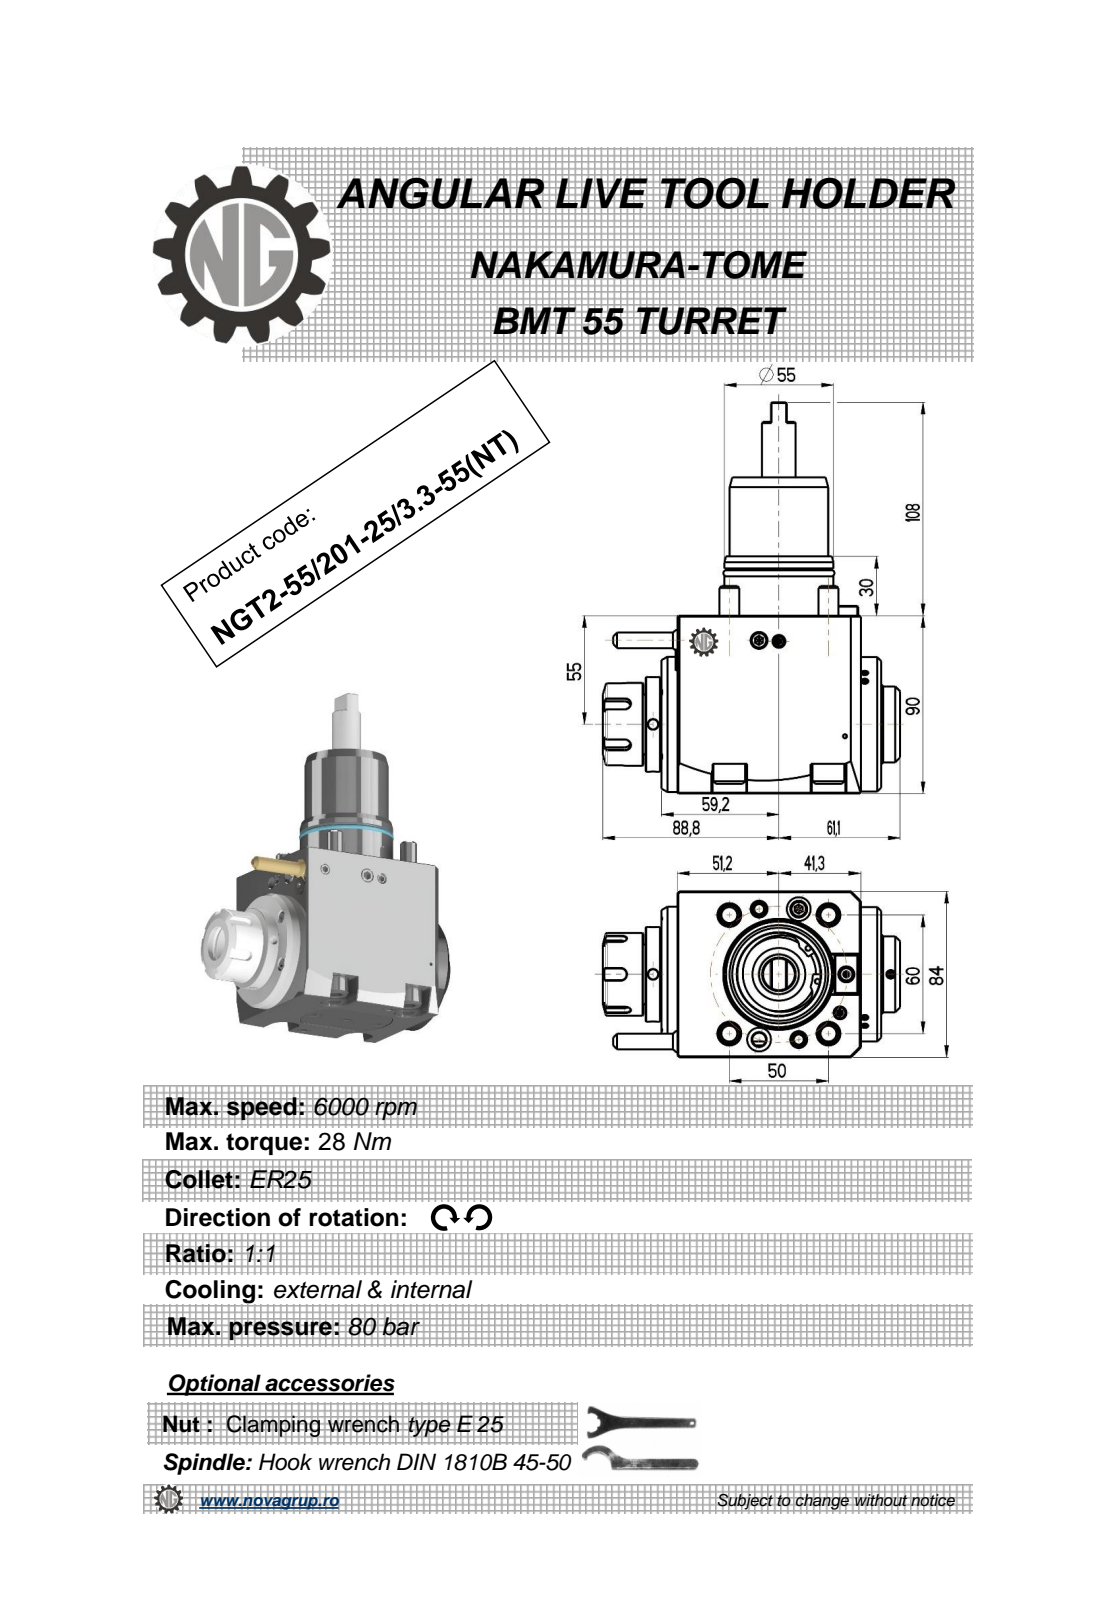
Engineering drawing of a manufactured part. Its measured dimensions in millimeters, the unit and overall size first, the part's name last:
Units: millimetres
Overall size (bounding box): 198 × 149.9 × 84
Round holes (diameter × count): ⌀5 ×3, ⌀6.8 ×2, ⌀3 ×1, ⌀20.3 ×1
Round bosses / shafts (diameter × count): ⌀16 ×4, ⌀10 ×4, ⌀68.5 ×1, ⌀68 ×1, ⌀55 ×1, ⌀50 ×1, ⌀49.7 ×1, ⌀48 ×1
Partial cylindrical surfaces — rounded edges, fillets, slot ends (radius × count): R0.32 ×20, R0.22 ×6, R3 ×5, R8.5 ×4, R0.8 ×2, R390 ×2
Main face-to-face distances: 84, 90, 8, 92.5, 100.5, 110.8, 102.8, 10.3, 70, 160
Hole centre spacings: 54.43, 62.82, 68.96, 80.52
Volume: 961 048 mm³ · Surface area: 81 451 mm²
Bodies: 2 solids, 419 faces (187 planar, 109 cylindrical, 123 other)
Part name (STEP PRODUCT): NGT2_55_201_25_3_3_55_NT
STEP written by: PRO/ENGINEER BY PARAMETRIC TECHNOLOGY CORPORATION, 2010280 (CONFIG_CONTROL_DESIGN)
